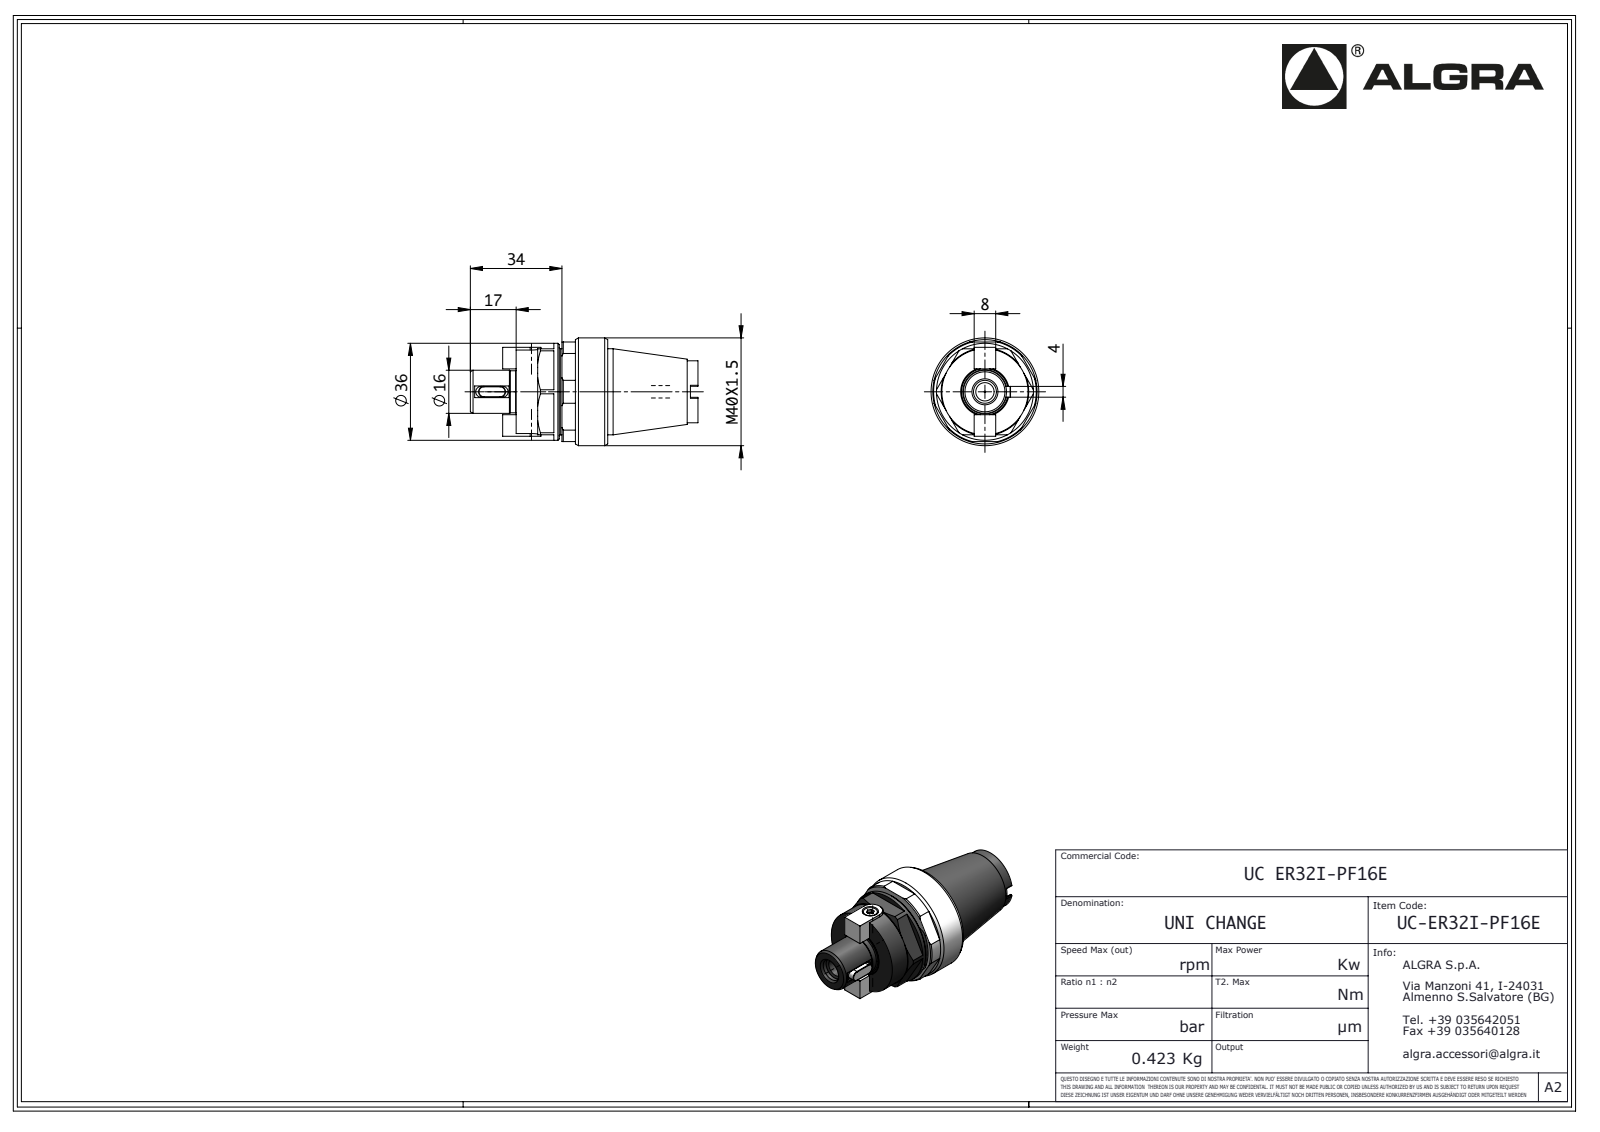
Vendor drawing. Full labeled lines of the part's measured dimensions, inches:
Part name (STEP PRODUCT): UC-ER32I-PF16E
STEP written by: SolidWorks 2016 (AUTOMOTIVE_DESIGN)
Units: inches
Bodies: 0 solids, 194 faces (100 planar, 62 cylindrical, 32 other)
Overall size (bounding box): 3.327 × 1.575 × 1.575
Round holes (diameter × count): ⌀0.043 ×2, ⌀0.098 ×2, ⌀0.059 ×1, ⌀0.197 ×1, ⌀0.236 ×1, ⌀0.268 ×1, ⌀0.335 ×1, ⌀1.262 ×1
Round bosses / shafts (diameter × count): ⌀0.067 ×2, ⌀1.575 ×1, ⌀1.417 ×1, ⌀1.26 ×1, ⌀1.258 ×1, ⌀0.906 ×1, ⌀0.63 ×1, ⌀0.614 ×1
Partial cylindrical surfaces — rounded edges, fillets, slot ends (radius × count): R0.012 ×8, R0.039 ×4, R0.079 ×4, R0.118 ×4, R0.006 ×2, R0.157 ×2, R0.222 ×2, R0.276 ×1
Main face-to-face distances: 0.669, 1.339, 0.315, 0.099, 1.355, 1.256, 1.209, 1.878, 2.547, 0.551
Hole centre spacings: 0.742, 0.285, 0.685, 0.571, 1.37
